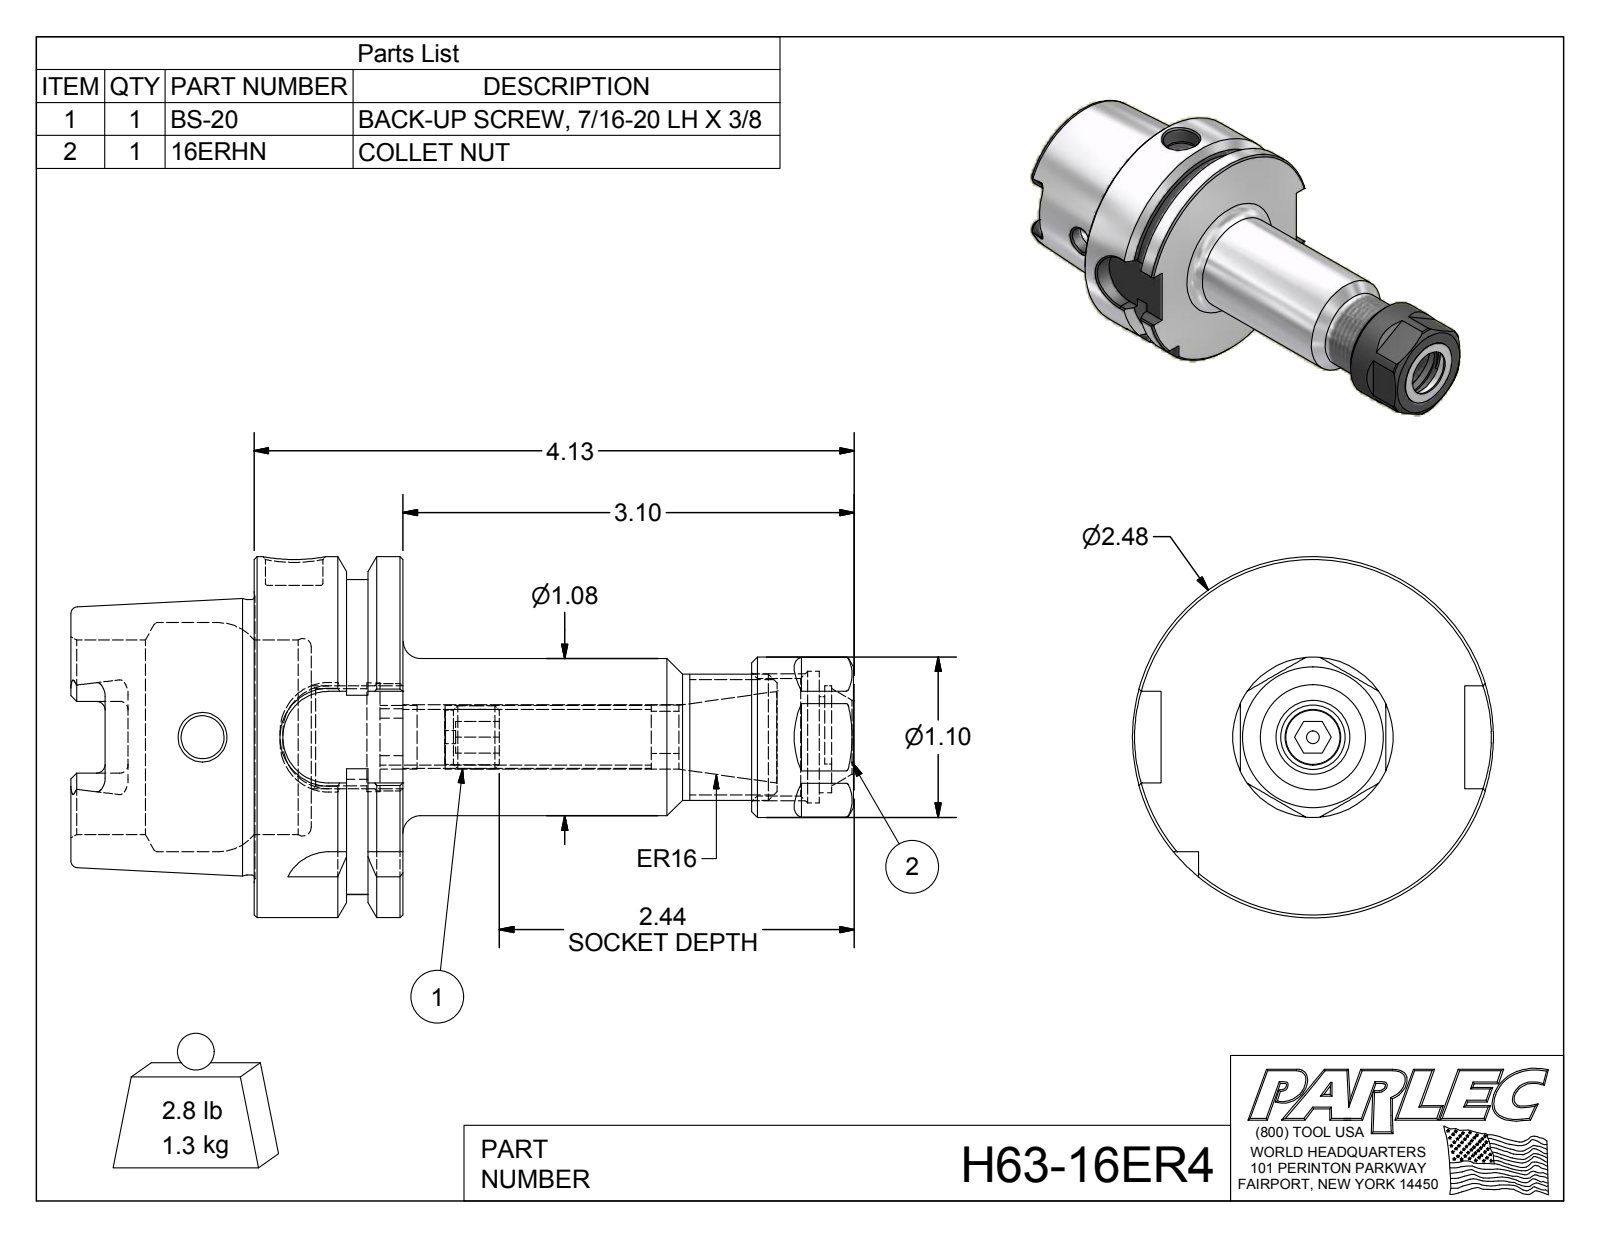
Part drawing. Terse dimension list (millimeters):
name: H63-16ER4; H63-16ER4-1; BS-20; 16ERHN
written by: Autodesk Inventor 2012 (AUTOMOTIVE_DESIGN)
unit: mm
bodies: 3 solids, 189 faces (84 planar, 46 cylindrical, 59 other)
size: 136.8 × 63 × 63
volume: 115 300 mm³; area: 33 850 mm²
holes: 1× ⌀2.3, 1× ⌀7.5, 1× ⌀9.7, 1× ⌀10, 1× ⌀11.2, 1× ⌀12.9, 1× ⌀16.8, 1× ⌀16.9, 1× ⌀19, 1× ⌀20.5, 1× ⌀23, 1× ⌀34
bosses: 1× ⌀63, 1× ⌀48, 1× ⌀28, 1× ⌀27.4, 1× ⌀22, 1× ⌀18.4, 1× ⌀11, 1× ⌀9.5
rounds: 6× R1.5, 4× R2.9, 4× R8, 1× R4.9, 1× R9, 1× R27.5
face distances: 26, 6.1, 9.9, 10, 16, 32, 42, 58, 51.9, 19.9
hole spacings: 1.3
